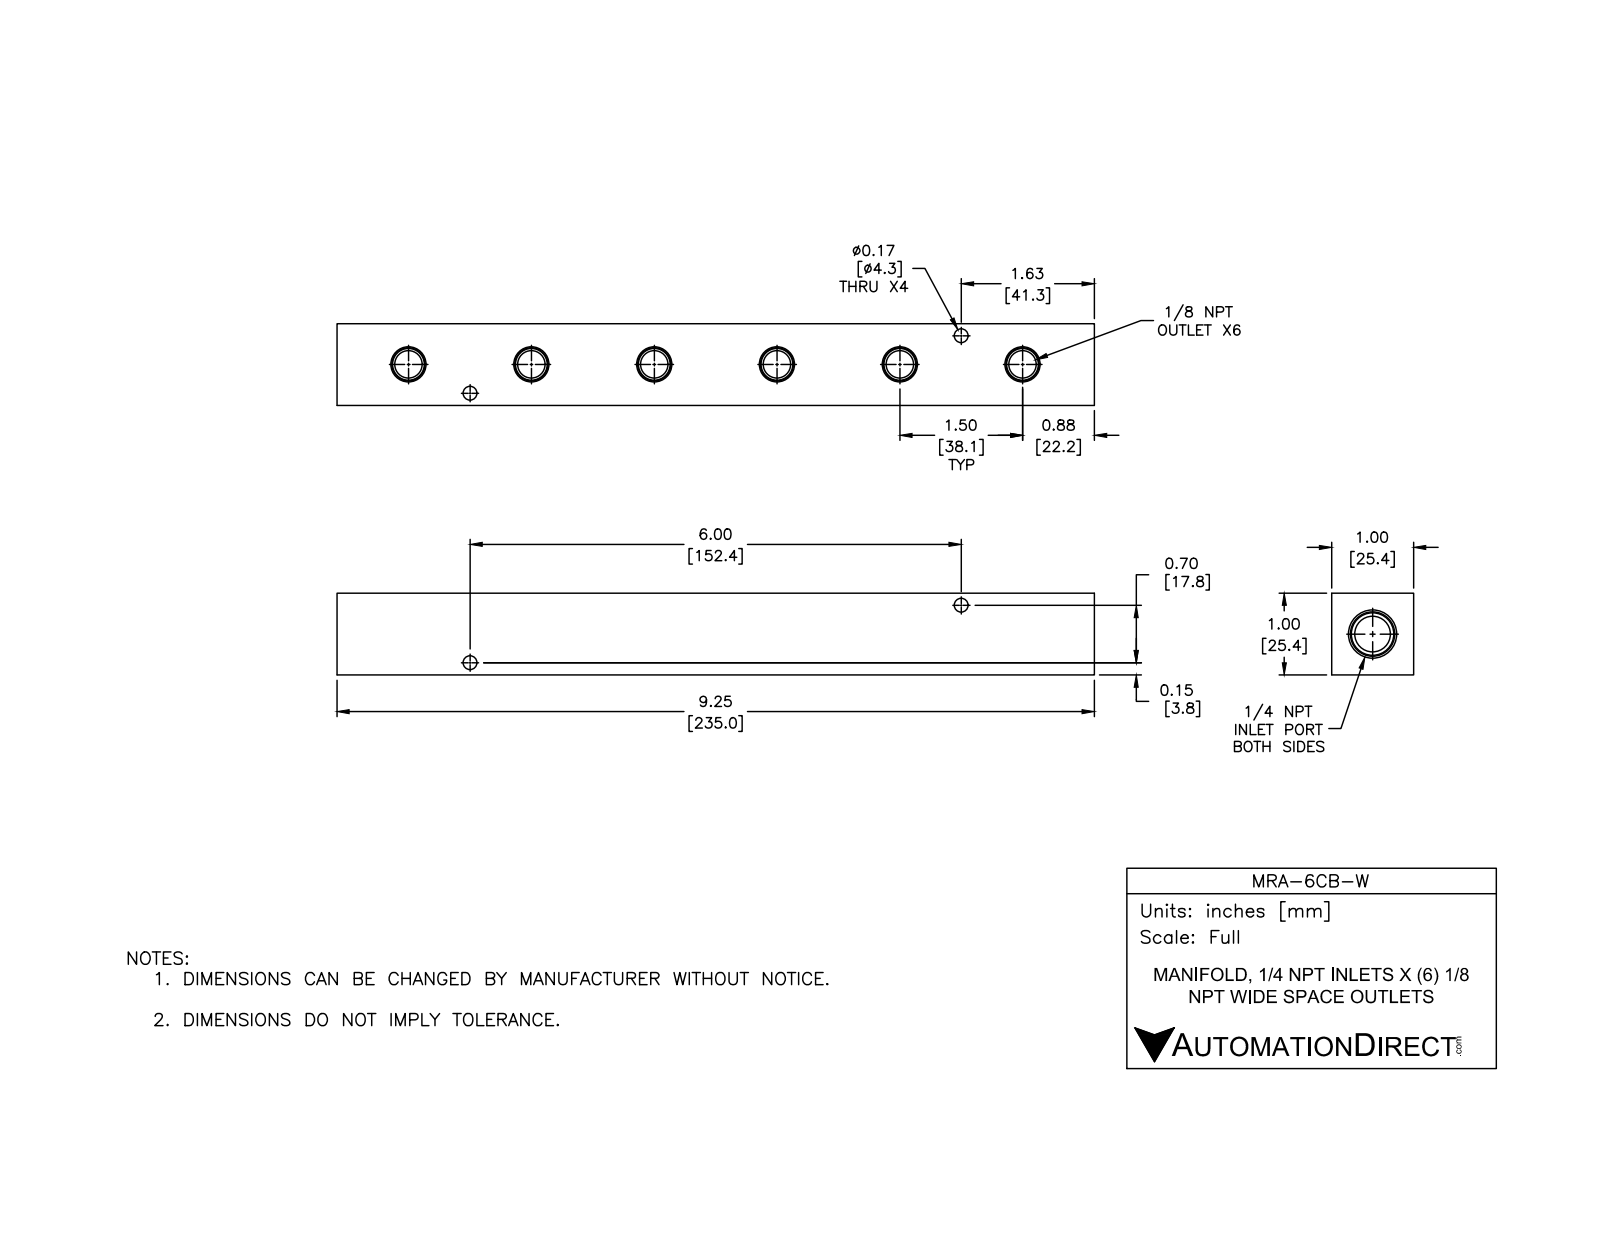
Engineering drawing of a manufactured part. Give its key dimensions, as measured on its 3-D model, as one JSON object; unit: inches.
{"part_name": "MRA-6CB-W", "step_written_by": "SolidWorks 2015 (CONFIG_CONTROL_DESIGN)", "units": "inches", "bodies": {"solids": 1, "faces": 76, "planar": 14, "cylindrical": 30, "other": 32}, "overall_size": [9.25, 1, 1], "volume_in3": 7.5, "surface_area_in2": 54.41, "round_holes": [[0.332, 6], [0.17, 4], [0.438, 1]], "face_to_face_distances": [1, 9.25, 0.73, 0.27, 0.39, 8.86, 8.47], "hole_center_spacings": [1.5, 0.828, 3, 4.5, 2.277, 3.766, 5.262, 6]}
